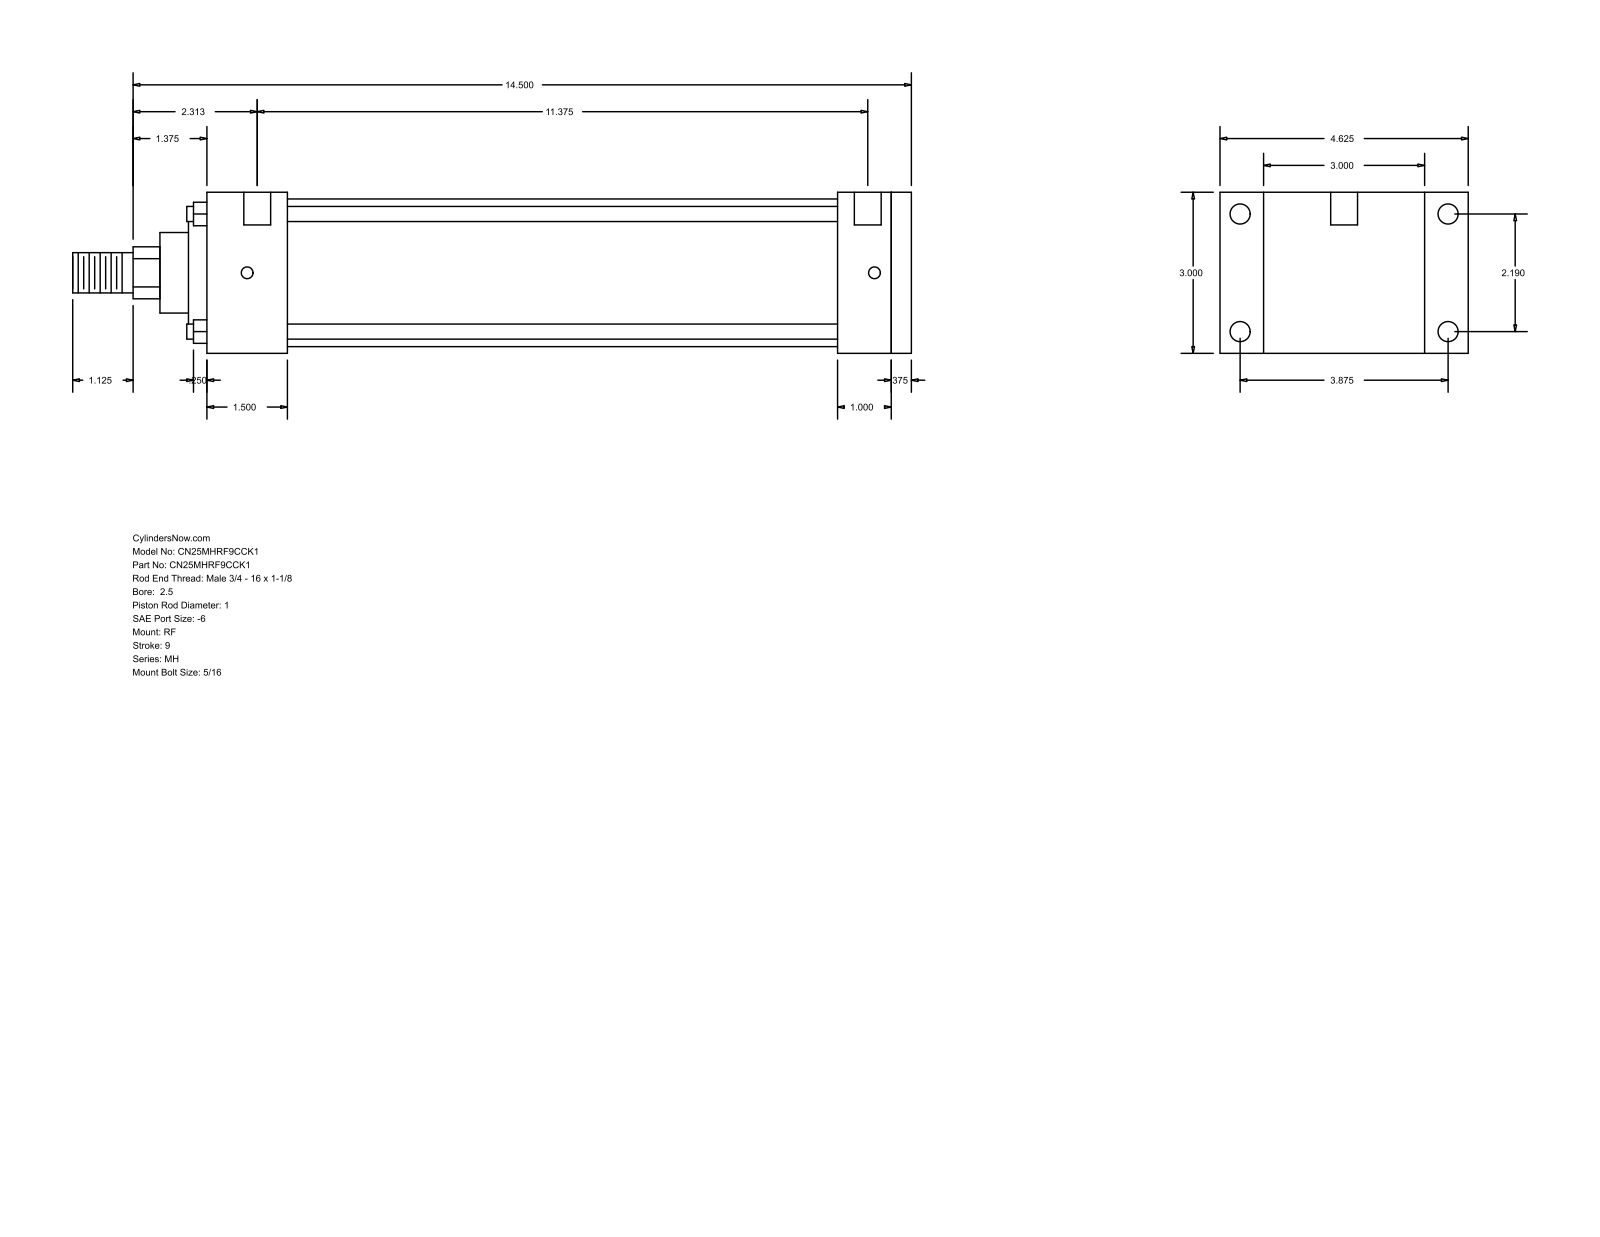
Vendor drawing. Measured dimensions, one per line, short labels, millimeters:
name: MH_RF__0250_1
written by: GSSL Pune (CONFIG_CONTROL_DESIGN)
unit: mm
bodies: 0 solids, 94 faces (65 planar, 29 cylindrical, 0 other)
size: 396.88 × 117.47 × 76.2
holes: 4× ⌀5.56, 4× ⌀9.53, 2× ⌀12.7
bosses: 4× ⌀7.14, 1× ⌀69.85, 1× ⌀60.33, 1× ⌀38.1, 1× ⌀25.4, 1× ⌀19.05
rounds: 1× R12.29
face distances: 76.2, 9.53, 333.38, 323.85, 34.92, 25.39, 298.46, 38.11, 260.35, 285.74
hole spacings: 55.62, 98.42, 113.05, 296.86, 3.18, 4.76, 288.92, 292.1
